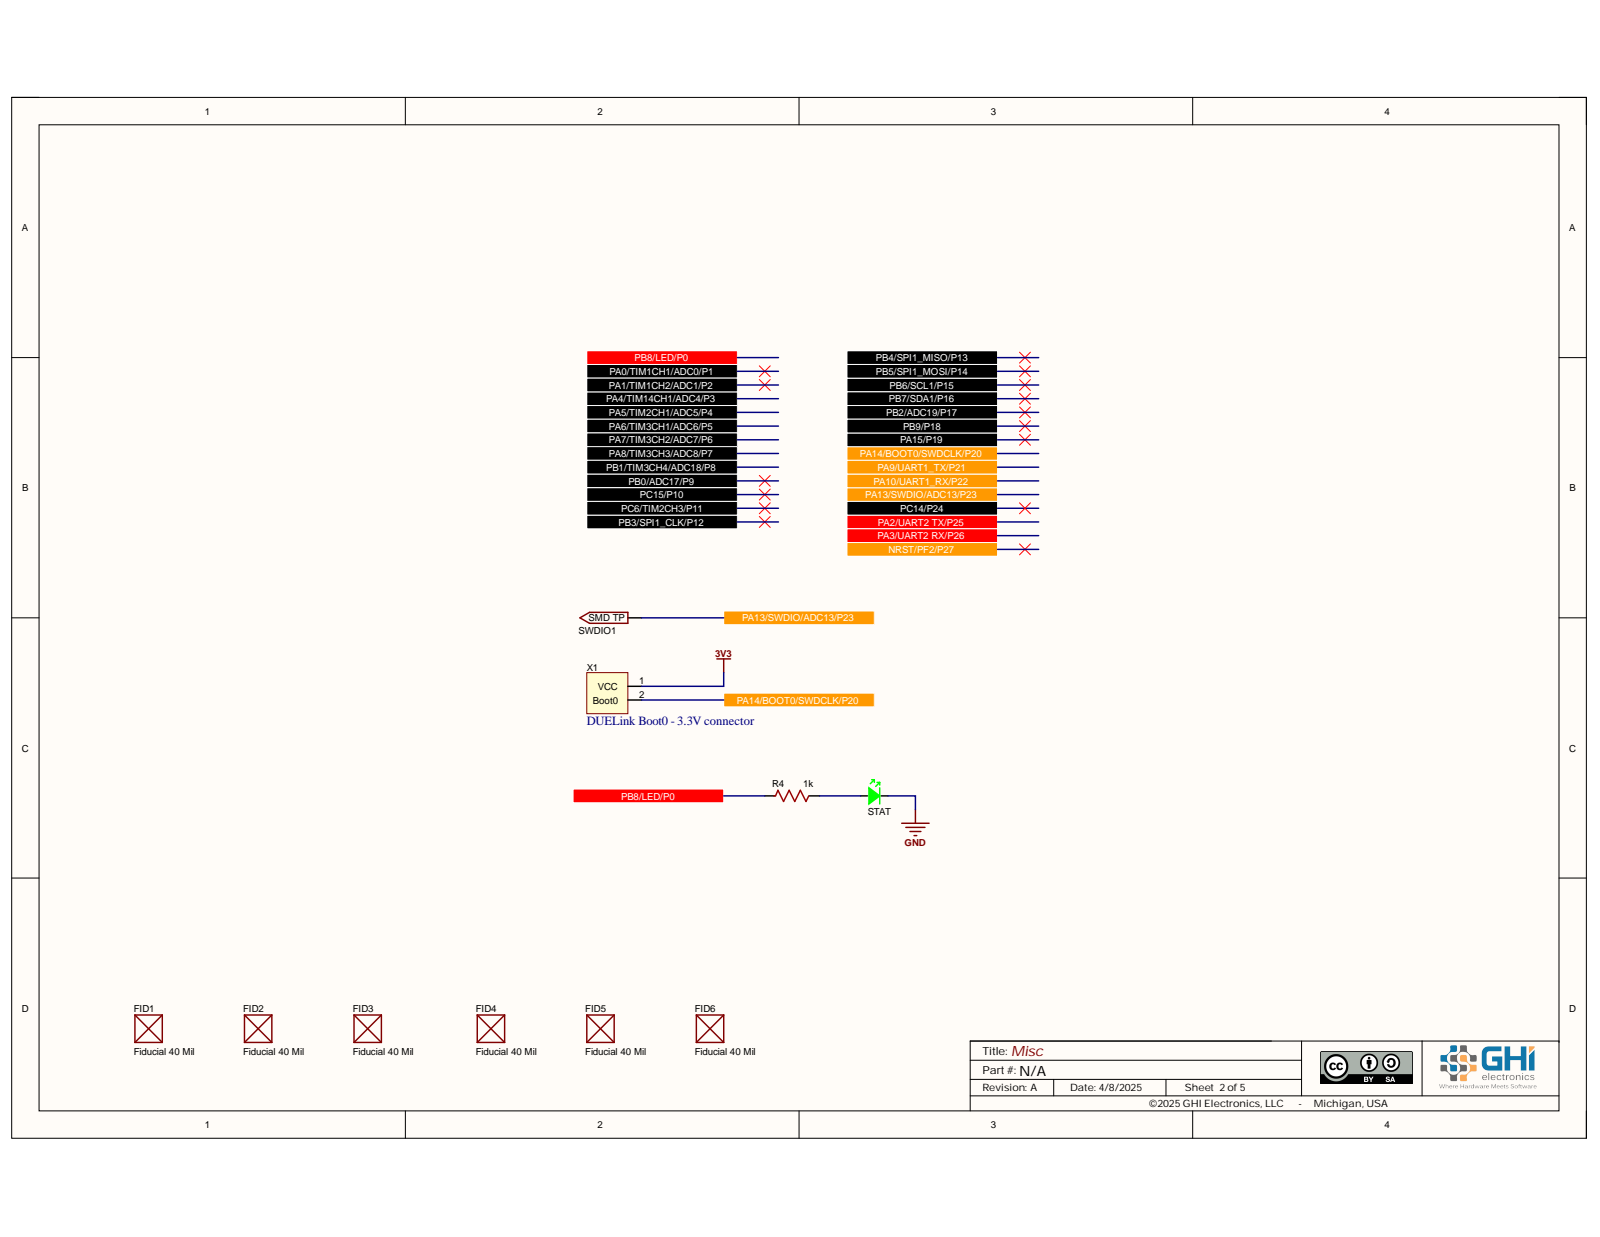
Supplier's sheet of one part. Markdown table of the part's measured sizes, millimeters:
| quantity | value |
| --- | --- |
| part name | PCB; Board; J10; Conn_Samtec_HTSW-104-07-G-D_eec (+7 more) |
| STEP written by | Open CASCADE 7.5 (AUTOMOTIVE_DESIGN) |
| units | millimeters |
| bodies | 170 solids, 2889 faces (2327 planar, 420 cylindrical, 142 other) |
| overall size | 51.5 × 50 × 48.33 |
| volume | 20 622 mm³ |
| surface area | 28 111 mm² |
| round holes (diameter × count) | 1.02 × 8, 3.2 × 6, 3.7 × 4, 1.02 × 2, 1.6 × 2, 3 × 2, 1 × 1, 6.8 × 1, 9.62 × 1 |
| round bosses / shafts (diameter × count) | 3.6 × 4, 4.5 × 2, 2.5 × 2, 10.12 × 1, 7.4 × 1 |
| partial cylindrical surfaces (radius × count) | 0.12 × 35, 0.5 × 16, 0.15 × 14, 2.61 × 7, 0.2 × 6, 0.3 × 6, 0.6 × 4, 0.17 × 2 |
| main face-to-face distances | 7, 14, 21, 1.6, 28, 35, 19.4, 42, 17.8, 9.9 |
| hole center spacings | 2.54, 40, 3.59, 5.08, 5.68, 4.95, 20.47, 7.62 |
